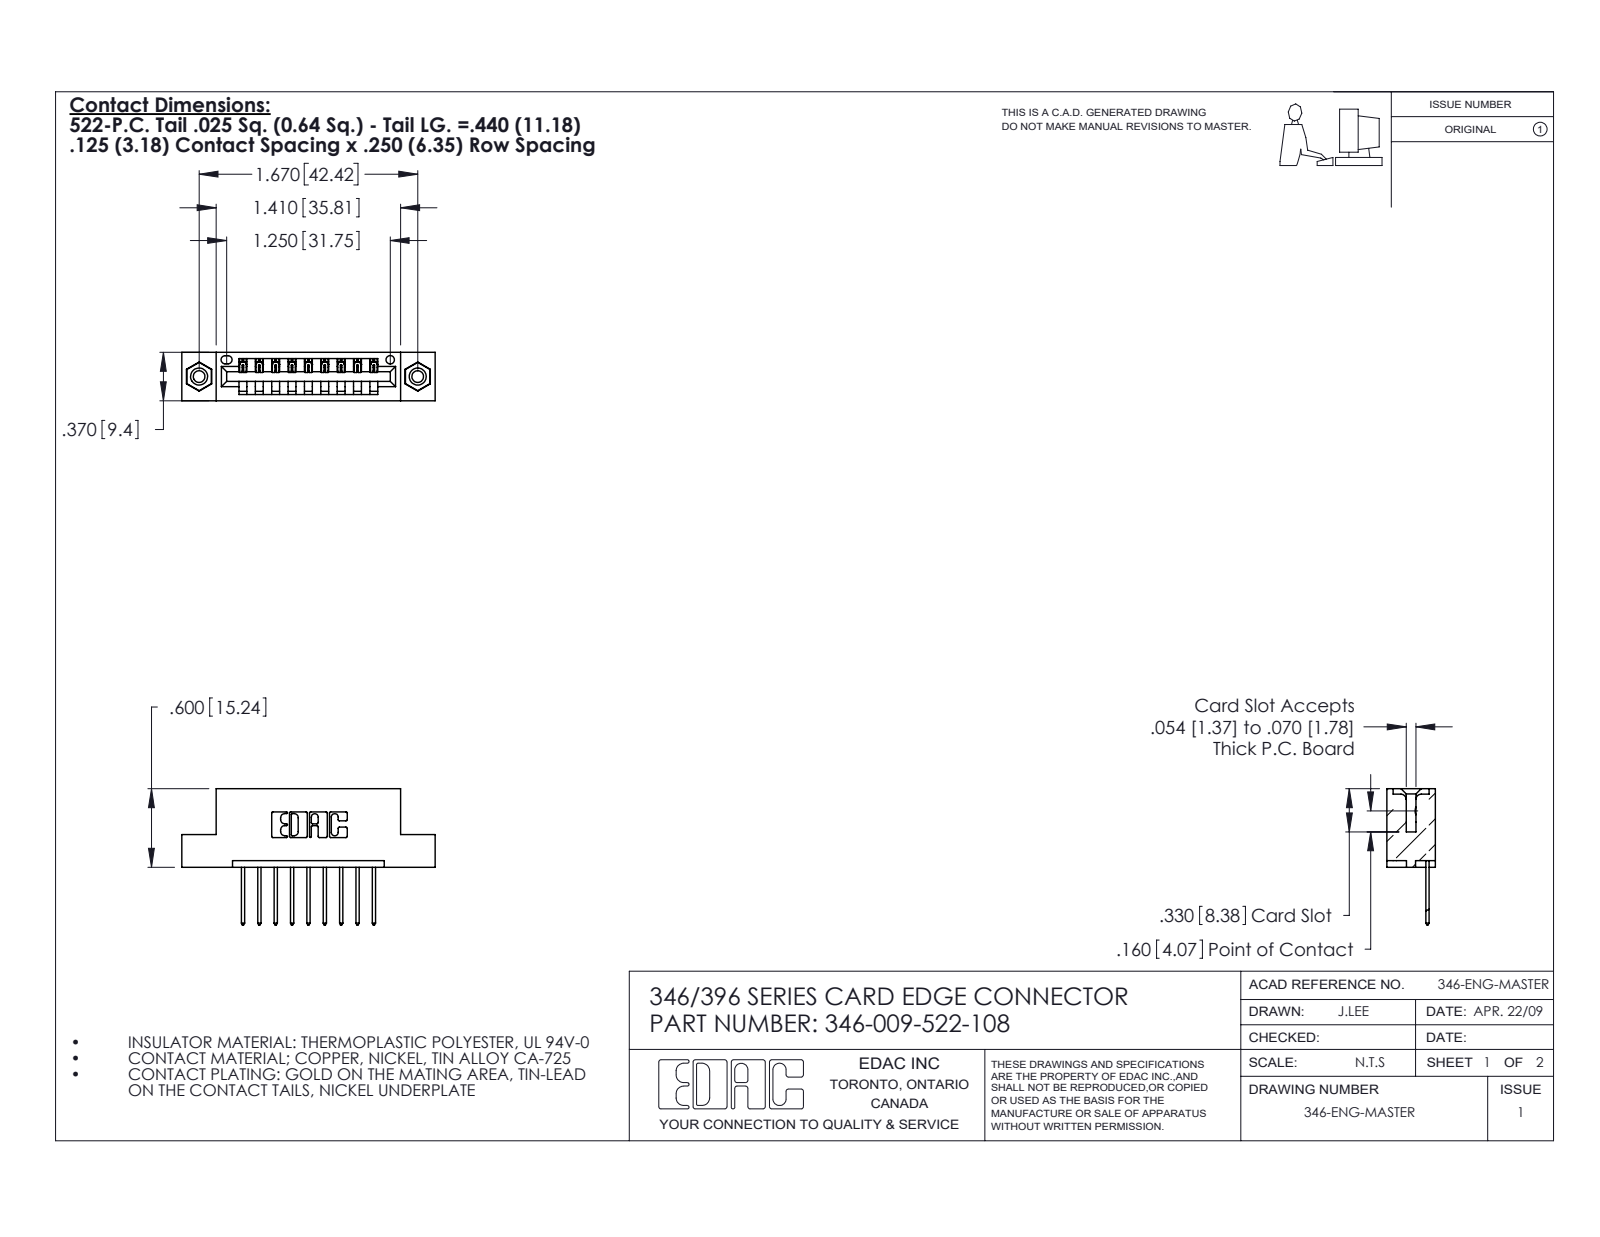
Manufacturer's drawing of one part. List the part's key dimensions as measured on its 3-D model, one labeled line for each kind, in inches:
Part name (STEP PRODUCT): 346 Part_Flush Mounting Lugs - 0.156 Dia-TI; 346-009-522-108; 345-292-001_345-293-122; 345-250-001_345-250-003-102
STEP written by: SolidWorks 2020 (CONFIG_CONTROL_DESIGN)
Units: inches
Bodies: 12 solids, 704 faces (468 planar, 220 cylindrical, 16 other)
Overall size (bounding box): 1.935 × 1.04 × 0.37
Volume: 0.273 in³ · Surface area: 8.197 in²
Round holes (diameter × count): ⌀0.089 ×2, ⌀0.125 ×2, ⌀0.156 ×2, ⌀0.064 ×1
Round bosses / shafts (diameter × count): ⌀0.155 ×2
Partial cylindrical surfaces — rounded edges, fillets, slot ends (radius × count): R0.01 ×22, R0.006 ×18, R0.01 ×18, R0.007 ×6, R0.031 ×6, R0.026 ×3, R0.031 ×2, R0.04 ×2
Main face-to-face distances: 0.25, 0.048, 0.322, 0.37, 0.072, 0.298, 0.025, 0.148, 0.222, 0.1
Hole centre spacings: 0.246, 1.465, 1.67
